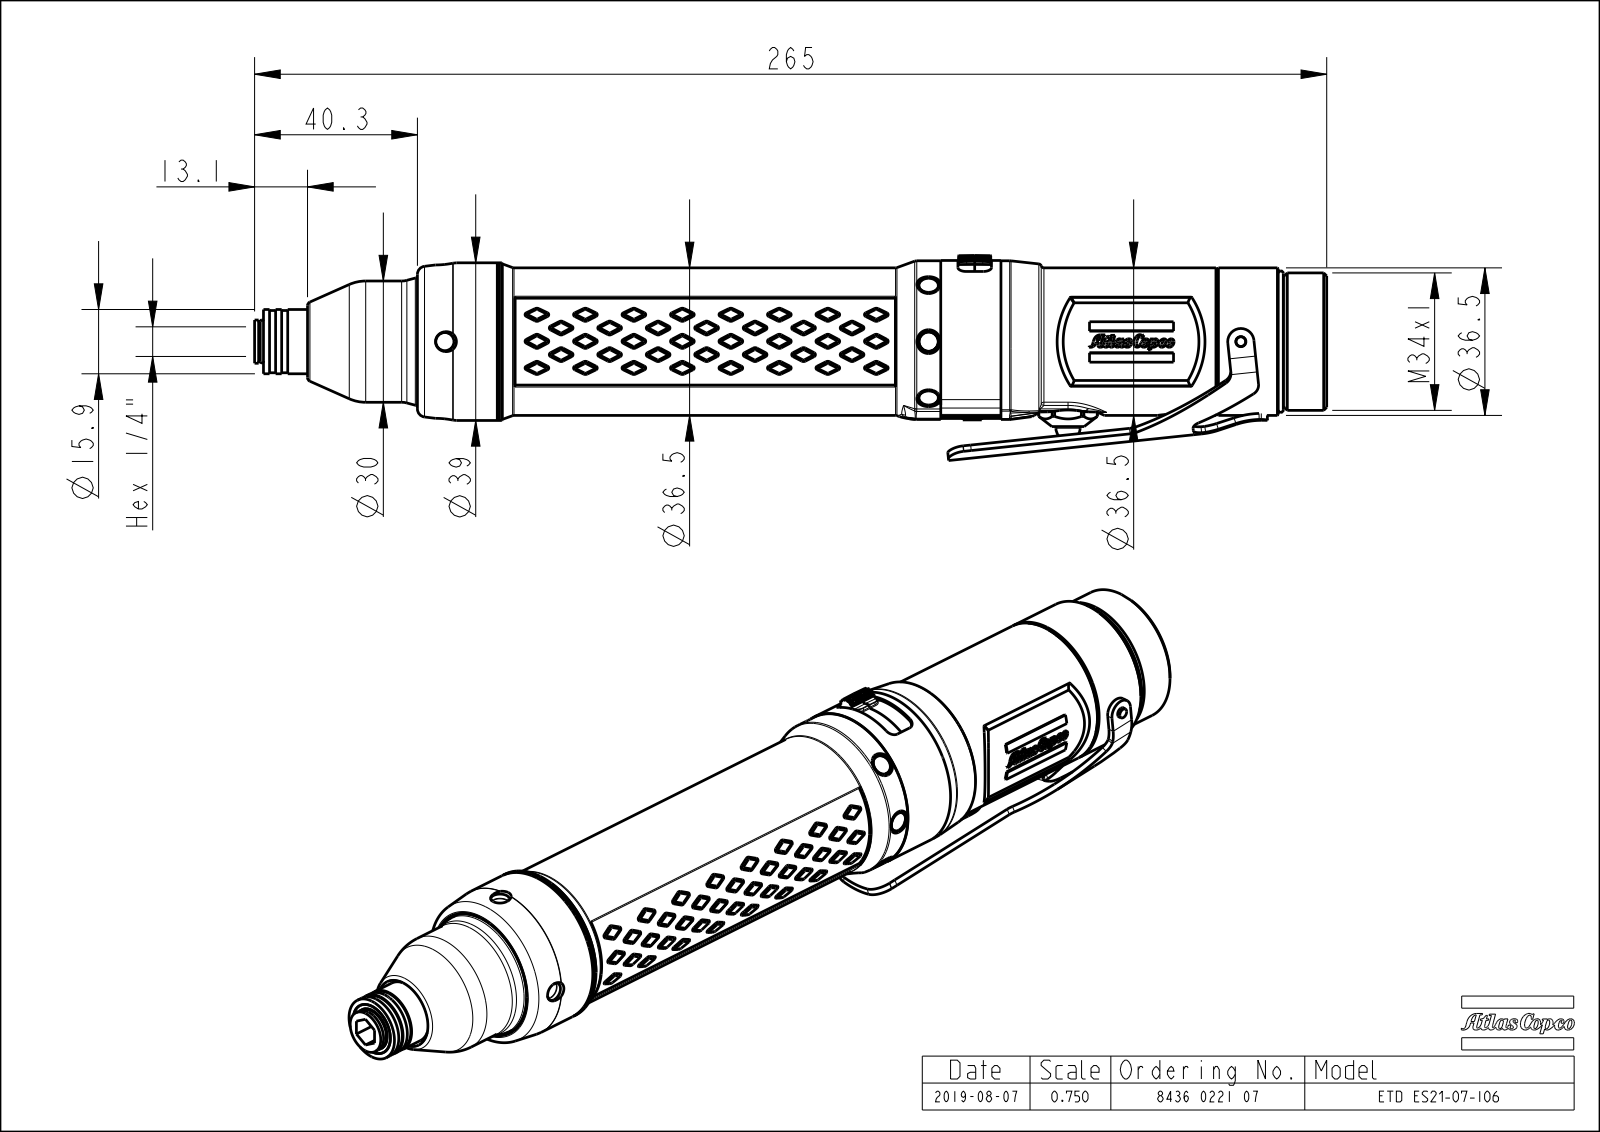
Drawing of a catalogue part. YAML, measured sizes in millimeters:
part_name: "MSBR-3; MSBR-2; MSBR-1; 8436022107_SW_SW0001_ASM"
step_written_by: "CREO PARAMETRIC BY PTC INC, 2018100 (CONFIG_CONTROL_DESIGN)"
units: millimeters
bodies: {solids: 17, faces: 2610, planar: 354, cylindrical: 504, other: 1752}
overall_size: [265.4, 50.7, 42.3]
volume: 262000
surface_area: 55340
round_holes:
  - {diameter: 5, count: 3}
  - {diameter: 2.5, count: 2}
  - {diameter: 4.5, count: 2}
  - {diameter: 6, count: 2}
  - {diameter: 2.7, count: 1}
  - {diameter: 3.3, count: 1}
  - {diameter: 5.5, count: 1}
  - {diameter: 12, count: 1}
  - {diameter: 14, count: 1}
  - {diameter: 16.5, count: 1}
  - {diameter: 17.5, count: 1}
  - {diameter: 18, count: 1}
round_bosses_or_shafts:
  - {diameter: 4.2, count: 3}
  - {diameter: 40, count: 1}
  - {diameter: 39, count: 1}
  - {diameter: 38, count: 1}
  - {diameter: 37.2, count: 1}
  - {diameter: 36.5, count: 1}
  - {diameter: 35, count: 1}
  - {diameter: 34, count: 1}
partial_cylinders:
  - {radius: 0.1, count: 37}
  - {radius: 1, count: 21}
  - {radius: 0.2, count: 16}
  - {radius: 0.3, count: 15}
  - {radius: 3, count: 14}
  - {radius: 1.6, count: 12}
  - {radius: 5, count: 11}
  - {radius: 0.4, count: 8}
face_to_face_distances: [0.5, 167.6, 0.5, 14.9, 12, 251.2, 2.5, 166.1, 95.5, 83.5]
hole_center_spacings: [23.7, 25.1, 36.3, 48.8, 77.3, 119.7, 130.5, 154.2]
